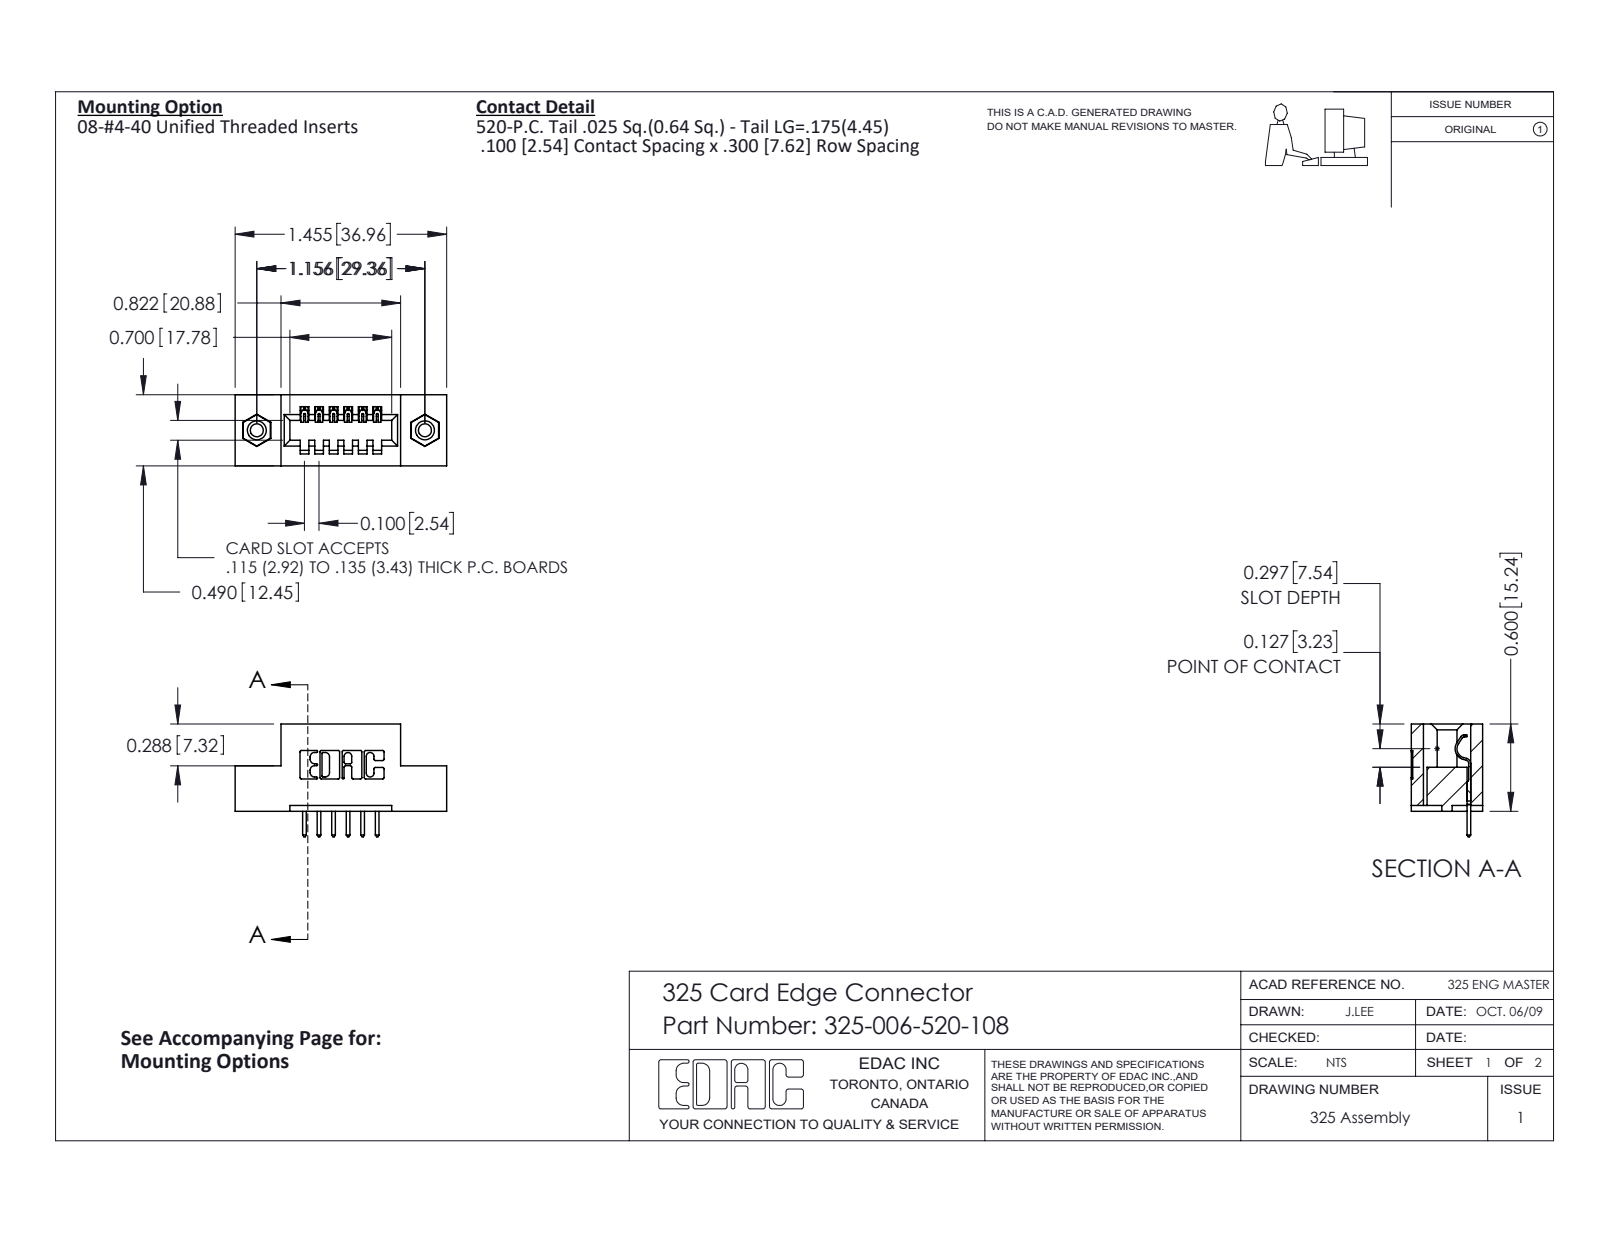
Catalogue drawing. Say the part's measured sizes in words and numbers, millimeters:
The part is named "325-006-520-108; 325 Part_TI; 345-250-001_345-250-003-102; 325-292-001_325-293-120". Its 3-D file was written by "SolidWorks 2016 (CONFIG_CONTROL_DESIGN)". It is 9 solids with 522 faces: 354 planar, 152 cylindrical and 16 other. Overall it measures 37 by 19.7 by 12.4 millimeters. Its volume is 4 390 cubic millimeters and its surface area 4 134 square millimeters. Round holes: 2 of diameter 2.3, 2 of diameter 3.2, 2 of diameter 4.1. Round bosses or shafts: 2 of diameter 3.9. Partial cylindrical surfaces (rounded edges, fillets, slot ends): 22 of radius 0.3, 12 of radius 0.2, 12 of radius 0.3, 6 of radius 0.2, 6 of radius 0.8, 3 of radius 0.7, 1 of radius 0.4, 1 of radius 0.6. The main face-to-face distances are 2.5, 7.6, 1, 12.4, 5.1, 2.1, 10.3, 1.5, 4.1, 8.1. The hole center spacings are 29.4.
